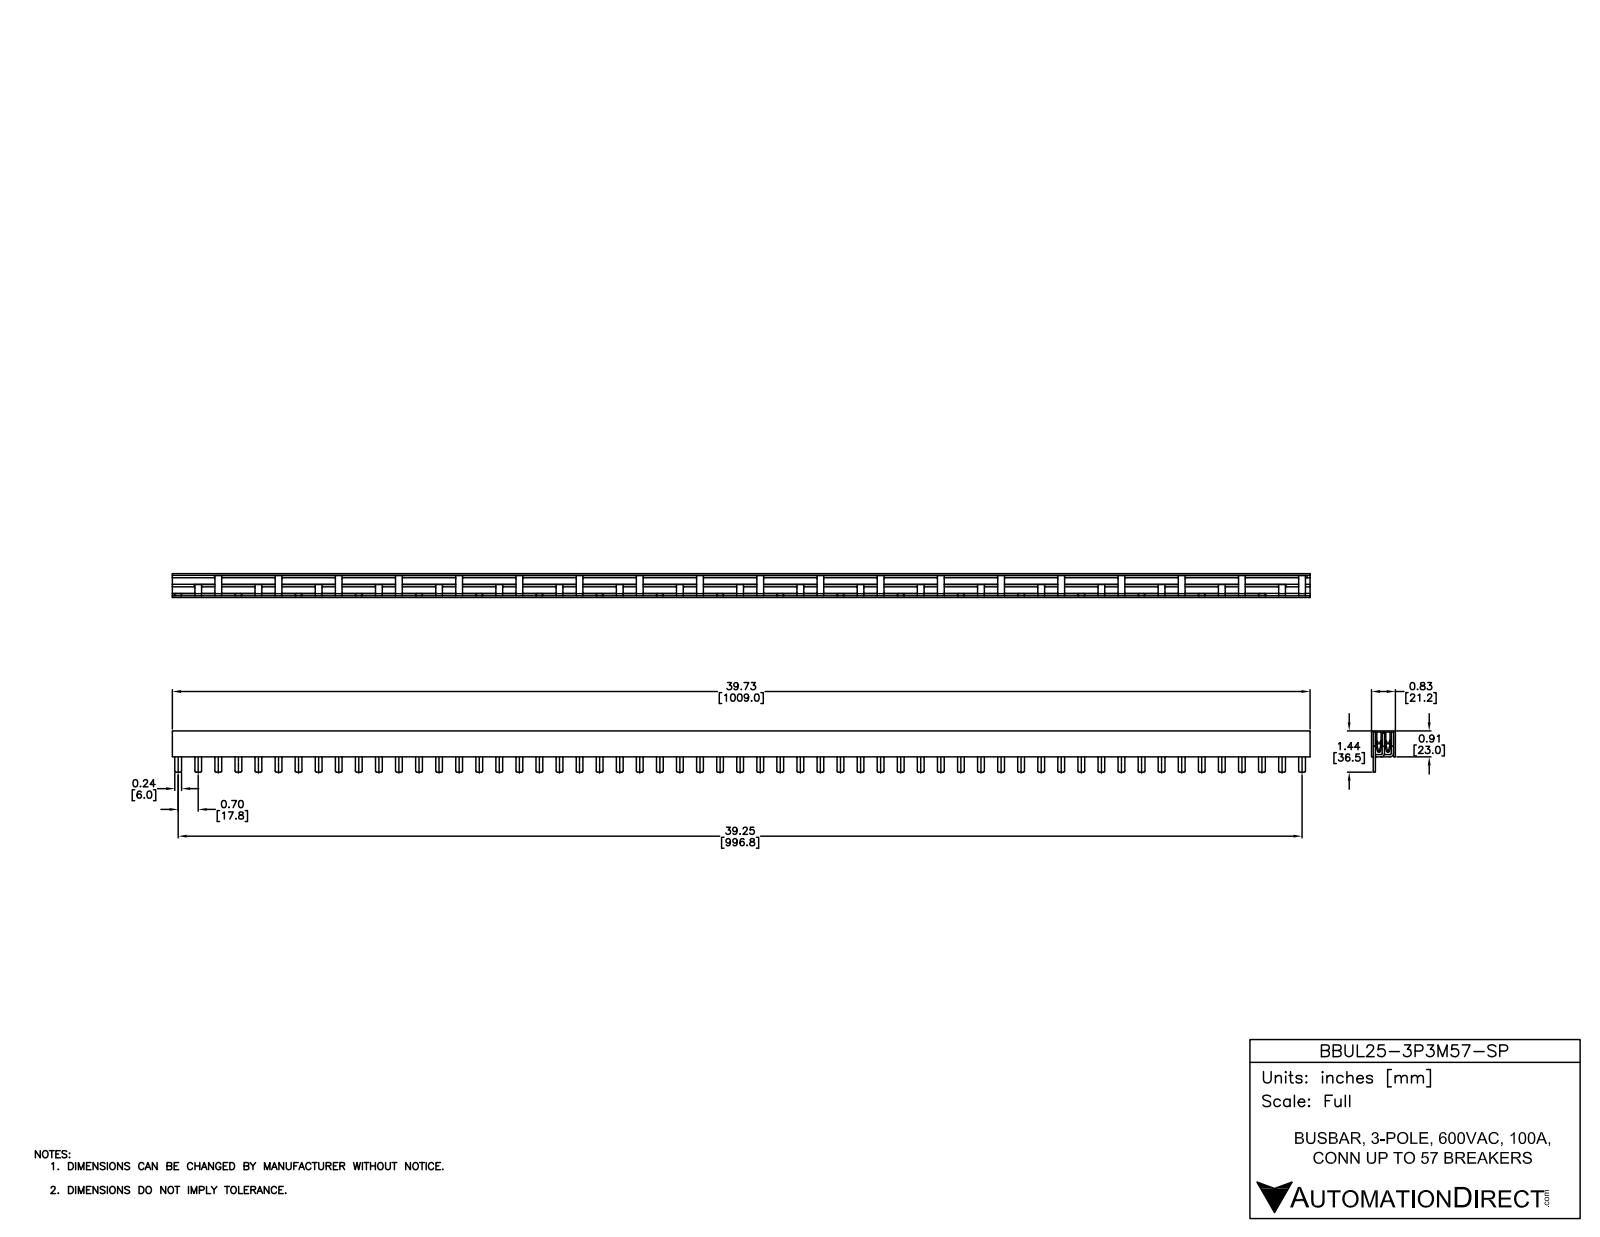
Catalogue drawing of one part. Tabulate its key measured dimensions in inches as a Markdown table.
| quantity | value |
| --- | --- |
| part name | BBUL25-3P-3M57-SP |
| STEP written by | SolidWorks 2014 (AUTOMOTIVE_DESIGN) |
| units | inches |
| bodies | 1 solid, 485 faces (291 planar, 194 cylindrical, 0 other) |
| overall size | 39.724 × 1.437 × 0.835 |
| volume | 30.56 in³ |
| surface area | 156.8 in² |
| partial cylindrical surfaces (radius × count) | 0.039 × 117, 0.012 × 2, 0.118 × 1 |
| main face-to-face distances | 0.835, 0.906, 0.776, 0.059, 0.697, 0.079, 0.138, 39.724, 0.531, 1.437 |
